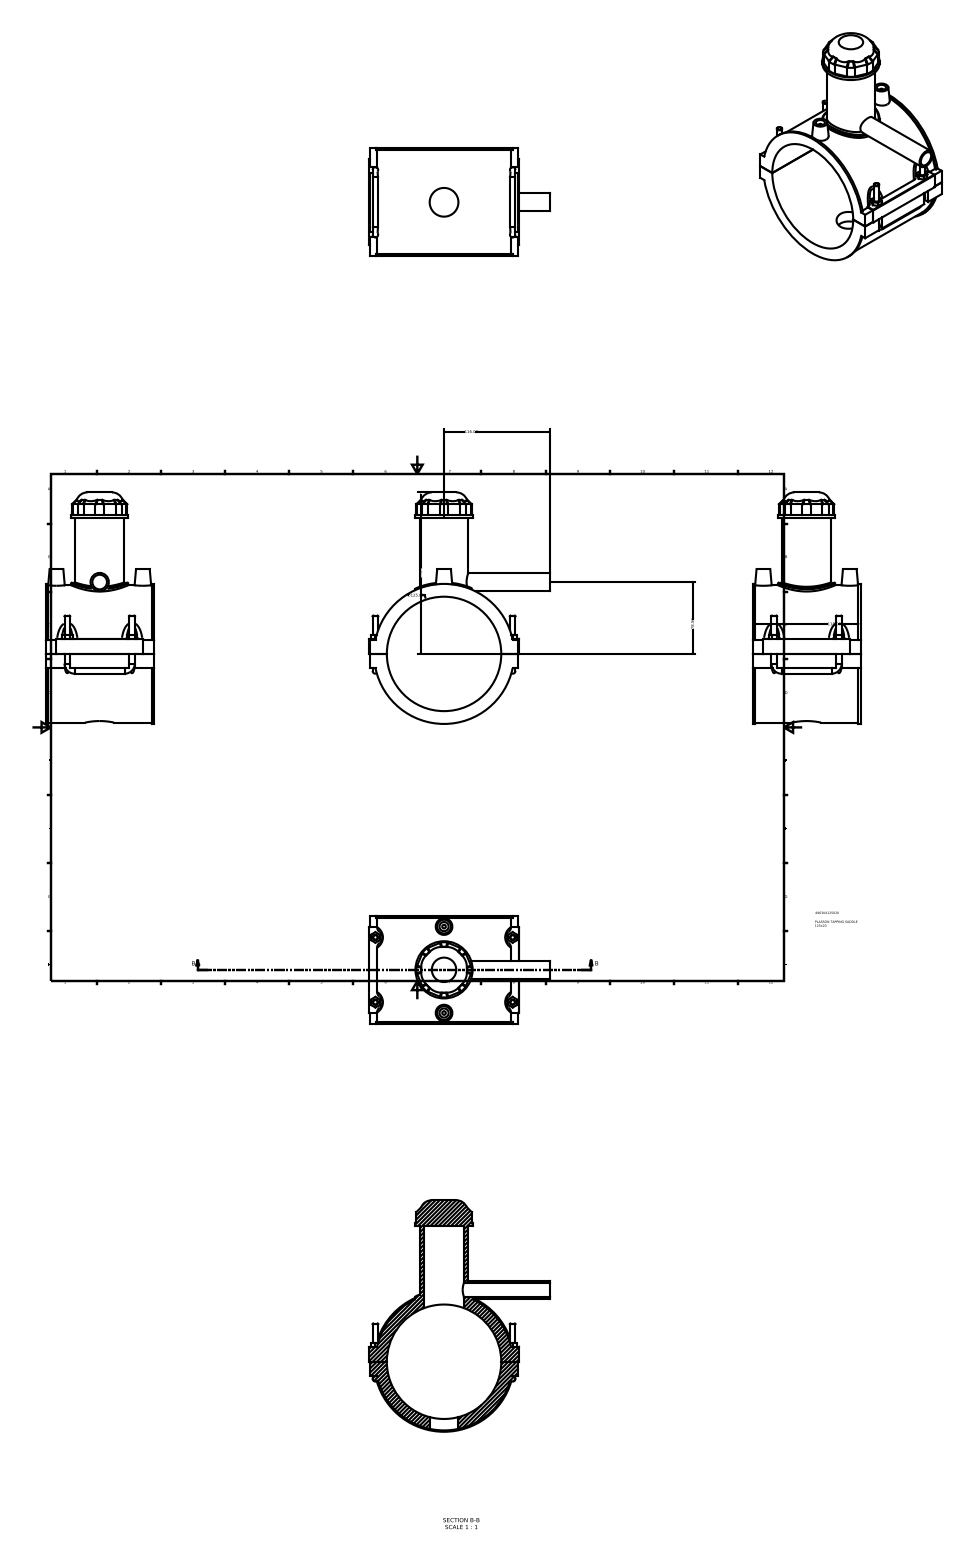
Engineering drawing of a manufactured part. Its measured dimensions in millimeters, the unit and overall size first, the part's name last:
Units: millimetres
Overall size (bounding box): 253 × 198 × 118
Round holes (diameter × count): ⌀10 ×2, ⌀16 ×1, ⌀31.36 ×1, ⌀43.75 ×1, ⌀125 ×1
Round bosses / shafts (diameter × count): ⌀6 ×4, ⌀4 ×2, ⌀153 ×1, ⌀150 ×1, ⌀62.5 ×1, ⌀53.12 ×1, ⌀20 ×1
Partial cylindrical surfaces — rounded edges, fillets, slot ends (radius × count): R12.5 ×8, R3 ×6, R7.5 ×4, R0.5 ×1, R78 ×1
Main face-to-face distances: 118, 1, 163, 148.05, 147.95, 162, 15.57, 15.67, 163.62, 32.25
Hole centre spacings: 47.2, 94.4
Volume: 805 835 mm³ · Surface area: 176 603 mm²
Bodies: 1 solid, 224 faces (125 planar, 55 cylindrical, 44 other)
Part name (STEP PRODUCT): 496304125020
STEP written by: Autodesk Inventor 2015 (AUTOMOTIVE_DESIGN)
